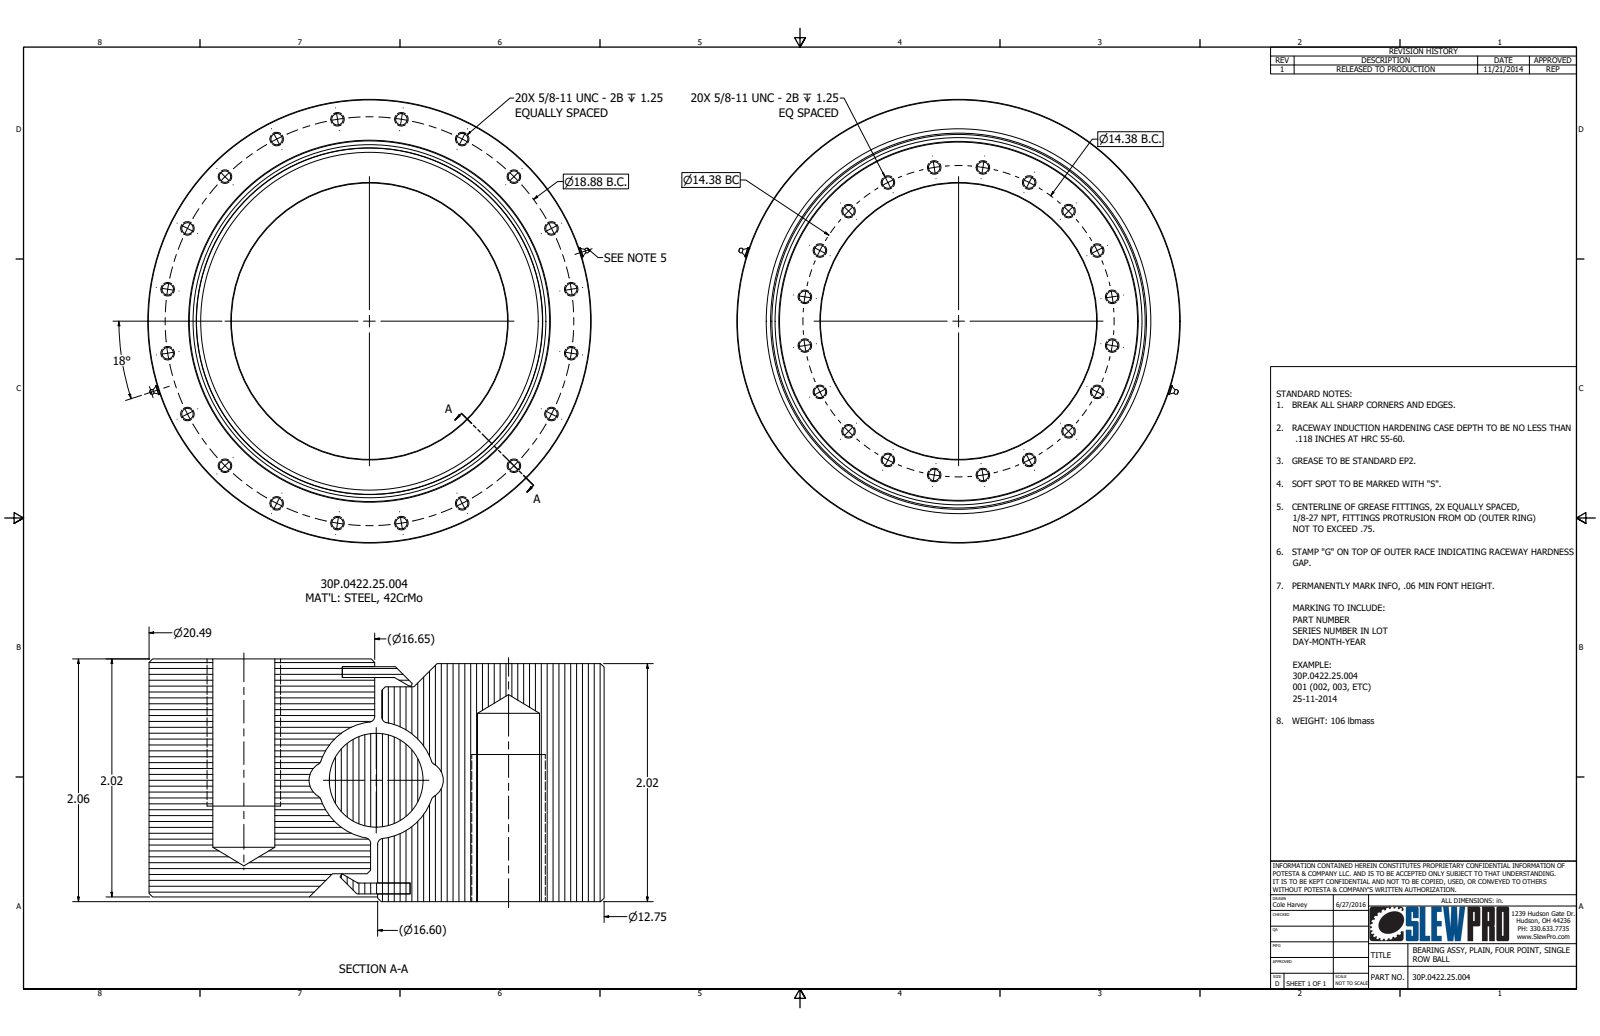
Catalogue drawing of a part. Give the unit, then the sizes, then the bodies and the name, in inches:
Units: inches
Overall size (bounding box): 20.486 × 20.486 × 2.062
Round holes (diameter × count): ⌀0.527 ×40, ⌀0.1 ×2, ⌀1.111 ×1, ⌀12.75 ×1, ⌀16.05 ×1, ⌀16.65 ×1, ⌀16.72 ×1, ⌀17.201 ×1
Round bosses / shafts (diameter × count): ⌀20.486 ×1, ⌀17.2 ×1, ⌀16.6 ×1, ⌀16.53 ×1, ⌀16.049 ×1, ⌀1.109 ×1
Main face-to-face distances: 0.04, 2.022, 2.062, 1.838, 1.982, 0.093, 0.066, 1.996, 0.026, 1.956
Hole centre spacings: 2.249, 4.442, 6.526, 7.187, 8.449, 10.165, 12.808, 14.198
Volume: 373.3 in³ · Surface area: 1 326 in²
Bodies: 7 solids, 298 faces (38 planar, 61 cylindrical, 199 other)
Part name (STEP PRODUCT): 30P.0422.25.001; 1_8 NPT Fitting
STEP written by: Autodesk Inventor 2026 (AUTOMOTIVE_DESIGN)
